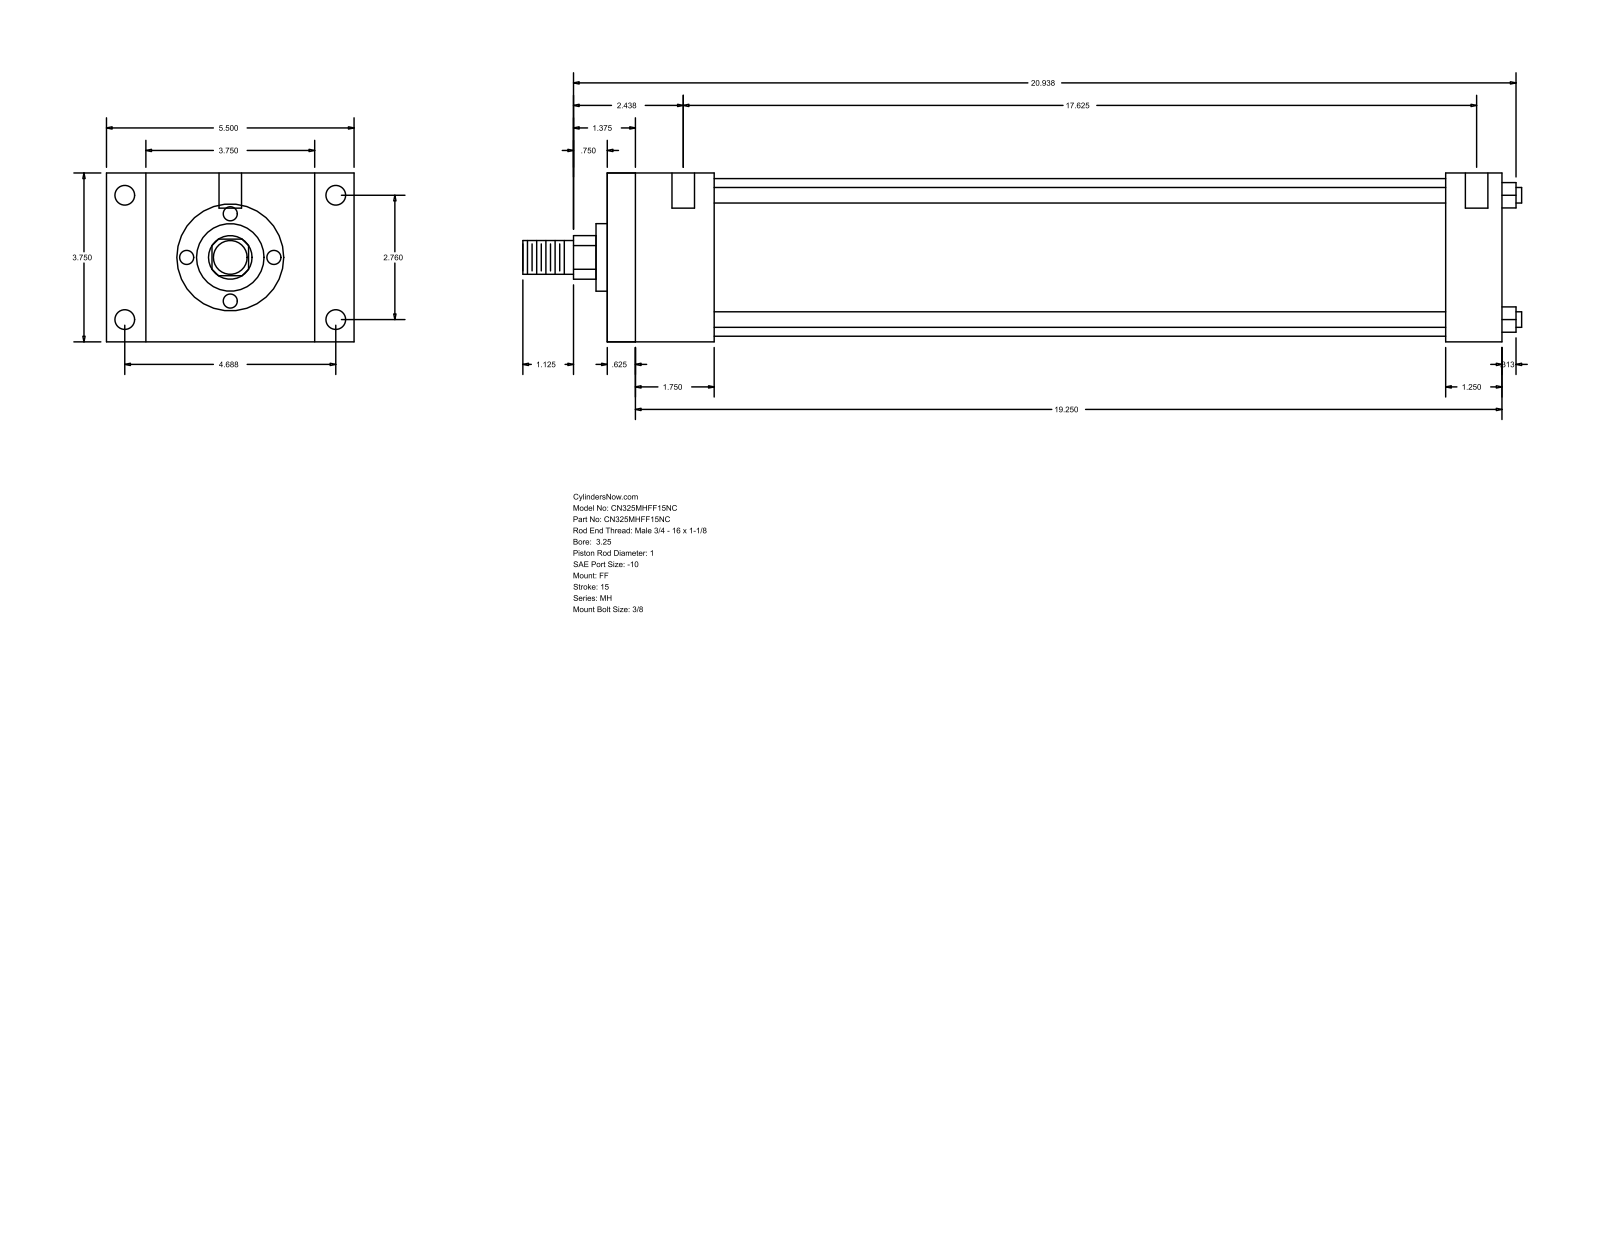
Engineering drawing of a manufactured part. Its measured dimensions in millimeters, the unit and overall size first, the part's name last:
Units: millimetres
Overall size (bounding box): 563.56 × 139.7 × 95.25
Round holes (diameter × count): ⌀5.56 ×4, ⌀11.13 ×4, ⌀12.7 ×2
Round bosses / shafts (diameter × count): ⌀8.76 ×4, ⌀88.9 ×1, ⌀38.1 ×1, ⌀25.4 ×1, ⌀19.05 ×1
Partial cylindrical surfaces — rounded edges, fillets, slot ends (radius × count): R12.29 ×1
Main face-to-face distances: 95.24, 504.83, 15.87, 488.96, 22.23, 117.47, 473.07, 457.2, 31.76, 60.33
Hole centre spacings: 70.1, 119.06, 138.16, 454.02, 1.58, 4.76, 447.68, 449.26
Bodies: 0 solids, 92 faces (64 planar, 28 cylindrical, 0 other)
Part name (STEP PRODUCT): MH_FF__0325_1
STEP written by: GSSL Pune (CONFIG_CONTROL_DESIGN)
